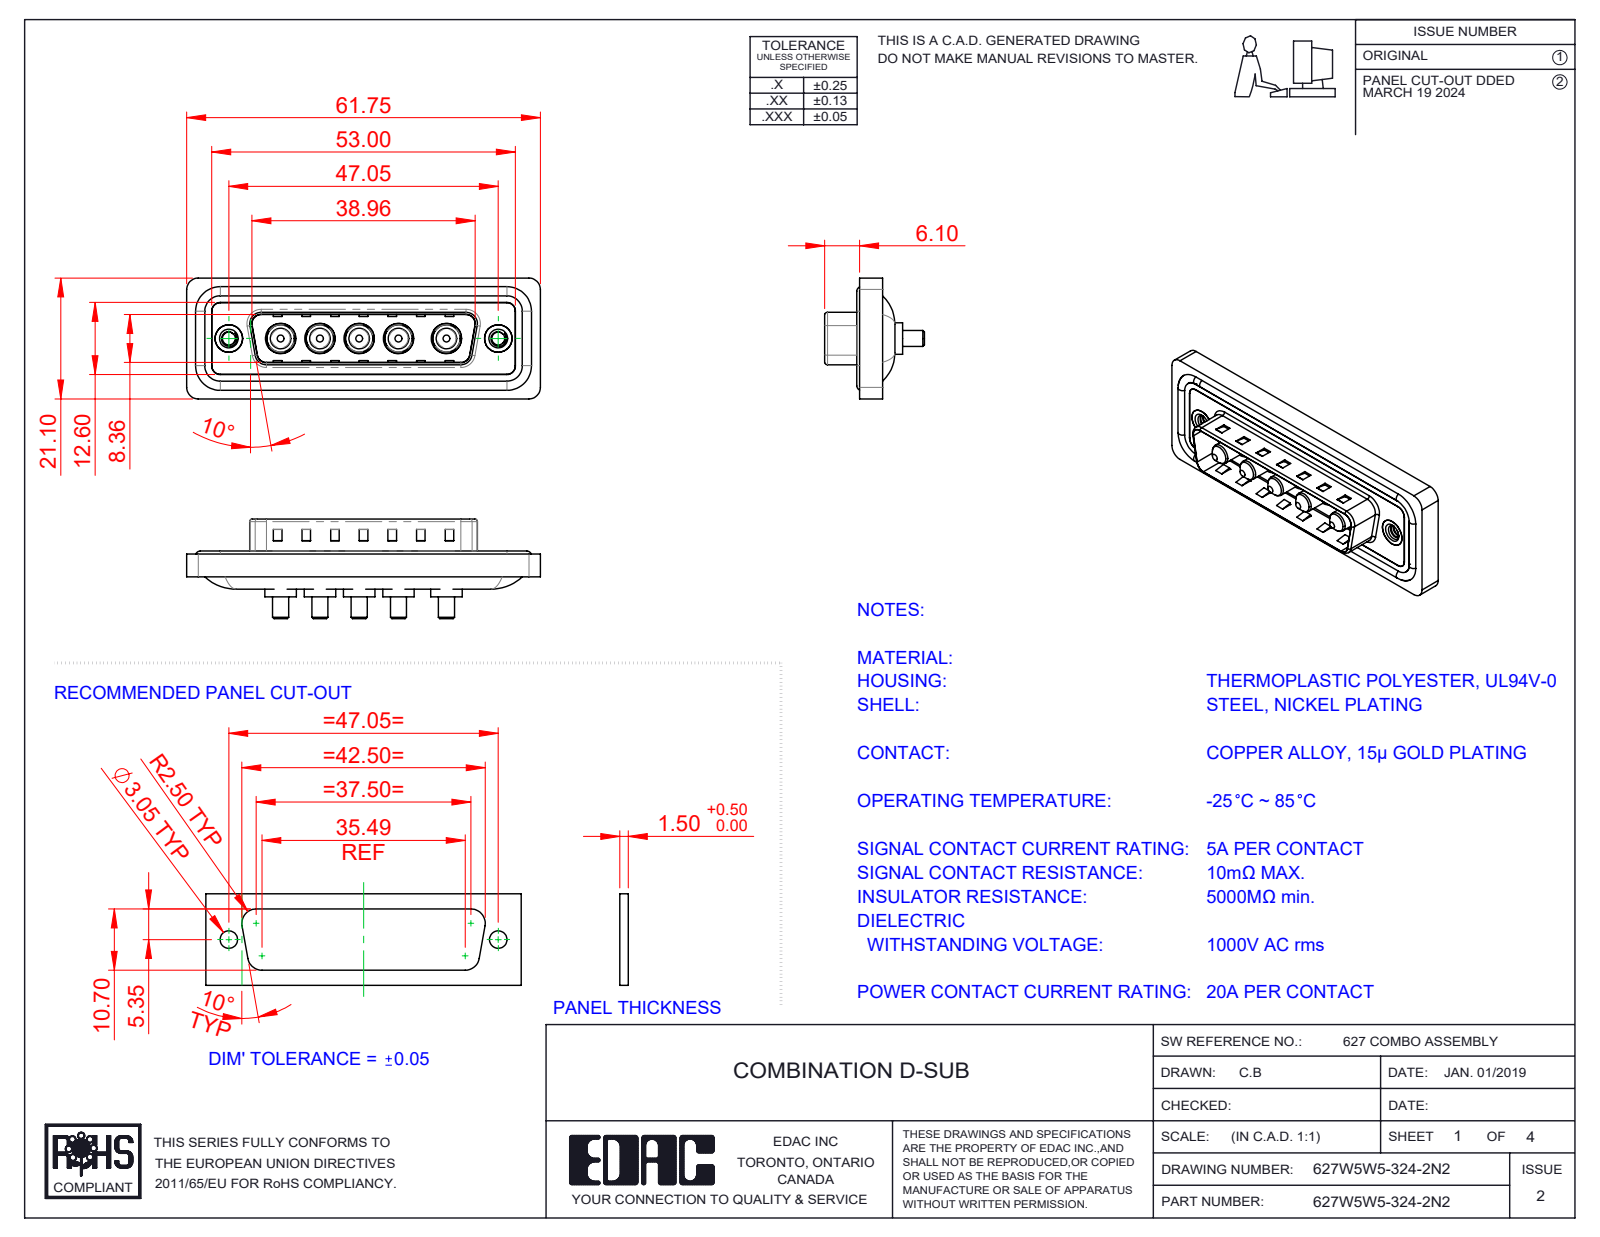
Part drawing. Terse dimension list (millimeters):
name: 627Combo Threaded Rivet_2; 627Combo Waterproof Housing_25 Contacts; 627Combo Shell Rear_25 Contacts; 627Combo Shell Front_25 Contacts (+3 more)
written by: SolidWorks 2023 (CONFIG_CONTROL_DESIGN)
unit: mm
bodies: 17 solids, 678 faces (259 planar, 283 cylindrical, 136 other)
size: 61.75 × 21.1 × 17.4
volume: 7 473 mm³; area: 11 796 mm²
holes: 5× ⌀4.85, 5× ⌀5.3, 2× ⌀2.26, 2× ⌀4, 2× ⌀4.8, 2× ⌀5
bosses: 5× ⌀5.5, 5× ⌀5.2, 5× ⌀4.75, 5× ⌀3.75, 5× ⌀3.6, 5× ⌀2.8, 4× ⌀1.6, 2× ⌀4.9
rounds: 22× R1.5, 18× R2, 8× R0.5, 8× R1.6, 5× R2.1, 4× R0.25, 4× R0.6, 4× R0.65
face distances: 0.4, 1.5, 0.5, 1.1, 3.1, 1.6, 2.9, 0.82, 9.58, 5.65
hole spacings: 6.86, 9.04, 13.73, 38.01, 6.87, 8.37, 8.38, 9.05
